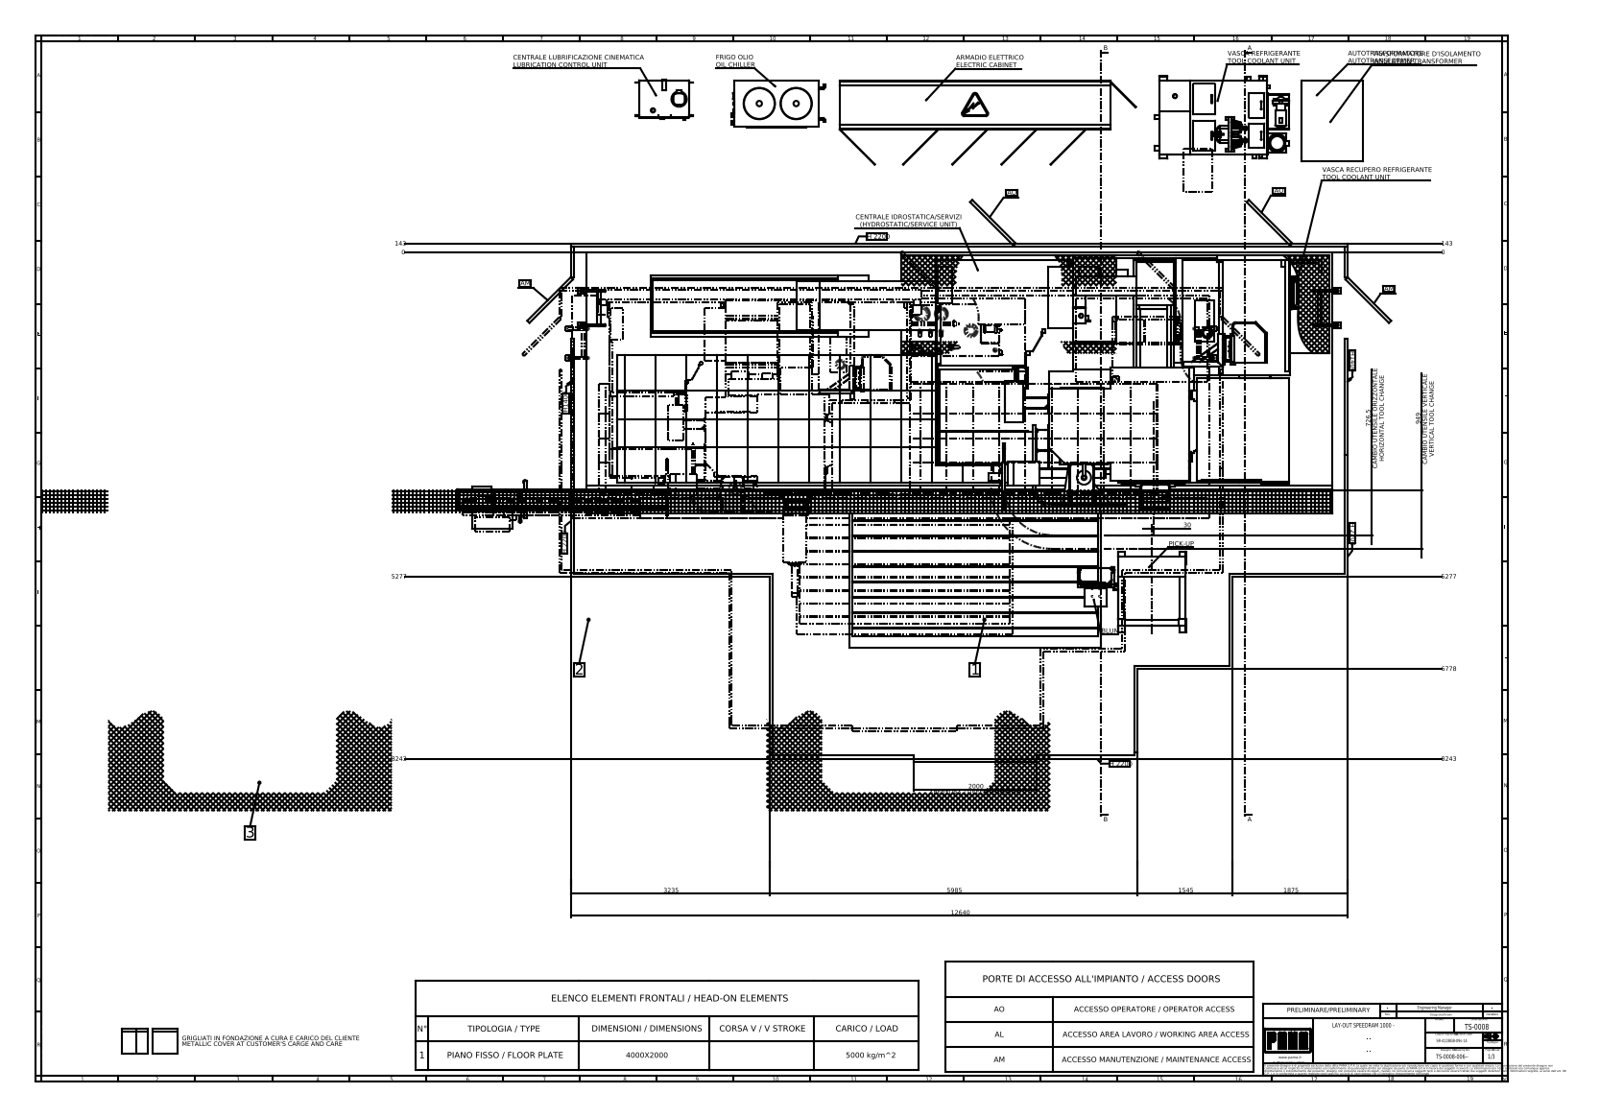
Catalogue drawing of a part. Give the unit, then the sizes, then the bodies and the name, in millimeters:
Units: millimetres
Overall size (bounding box): 16140 × 14057.4 × 7912.5
Round holes (diameter × count): ⌀35 ×64, ⌀69.6 ×63, ⌀37.2 ×18, ⌀30 ×9, ⌀13 ×8, ⌀14 ×8, ⌀8 ×6, ⌀12.5 ×4, ⌀56.66 ×4, ⌀60 ×4, ⌀25.6 ×3, ⌀50 ×3
Round bosses / shafts (diameter × count): ⌀42.4 ×18, ⌀20 ×14, ⌀40 ×11, ⌀9 ×10, ⌀55 ×8, ⌀66.3 ×7, ⌀60 ×6, ⌀35 ×6
Partial cylindrical surfaces — rounded edges, fillets, slot ends (radius × count): R5 ×128, R15 ×53, R8 ×52, R35 ×26, R6 ×25, R3 ×21, R4 ×21, R10 ×20
Main face-to-face distances: 2000, 50, 1247, 753, 5, 10, 13986, 16140, 2650, 2700
Hole centre spacings: 273.13, 500, 1235.56, 758.02, 1423.59, 1000, 130, 260
Volume: 412 000 000 000 mm³ · Surface area: 1 597 000 000 mm²
Bodies: 397 solids, 6335 faces (4445 planar, 1427 cylindrical, 463 other)
Part name (STEP PRODUCT): S001576_DEFAULT<A macchina>; S003241_Z=1200; BASAM.1400; S002726_ATC con utensili orizzontali; S003192_X=MIN; Y=MIN; Z=MIN; W=MIN (+8 more)
STEP written by: SolidWorks 2023 (AUTOMOTIVE_DESIGN)
